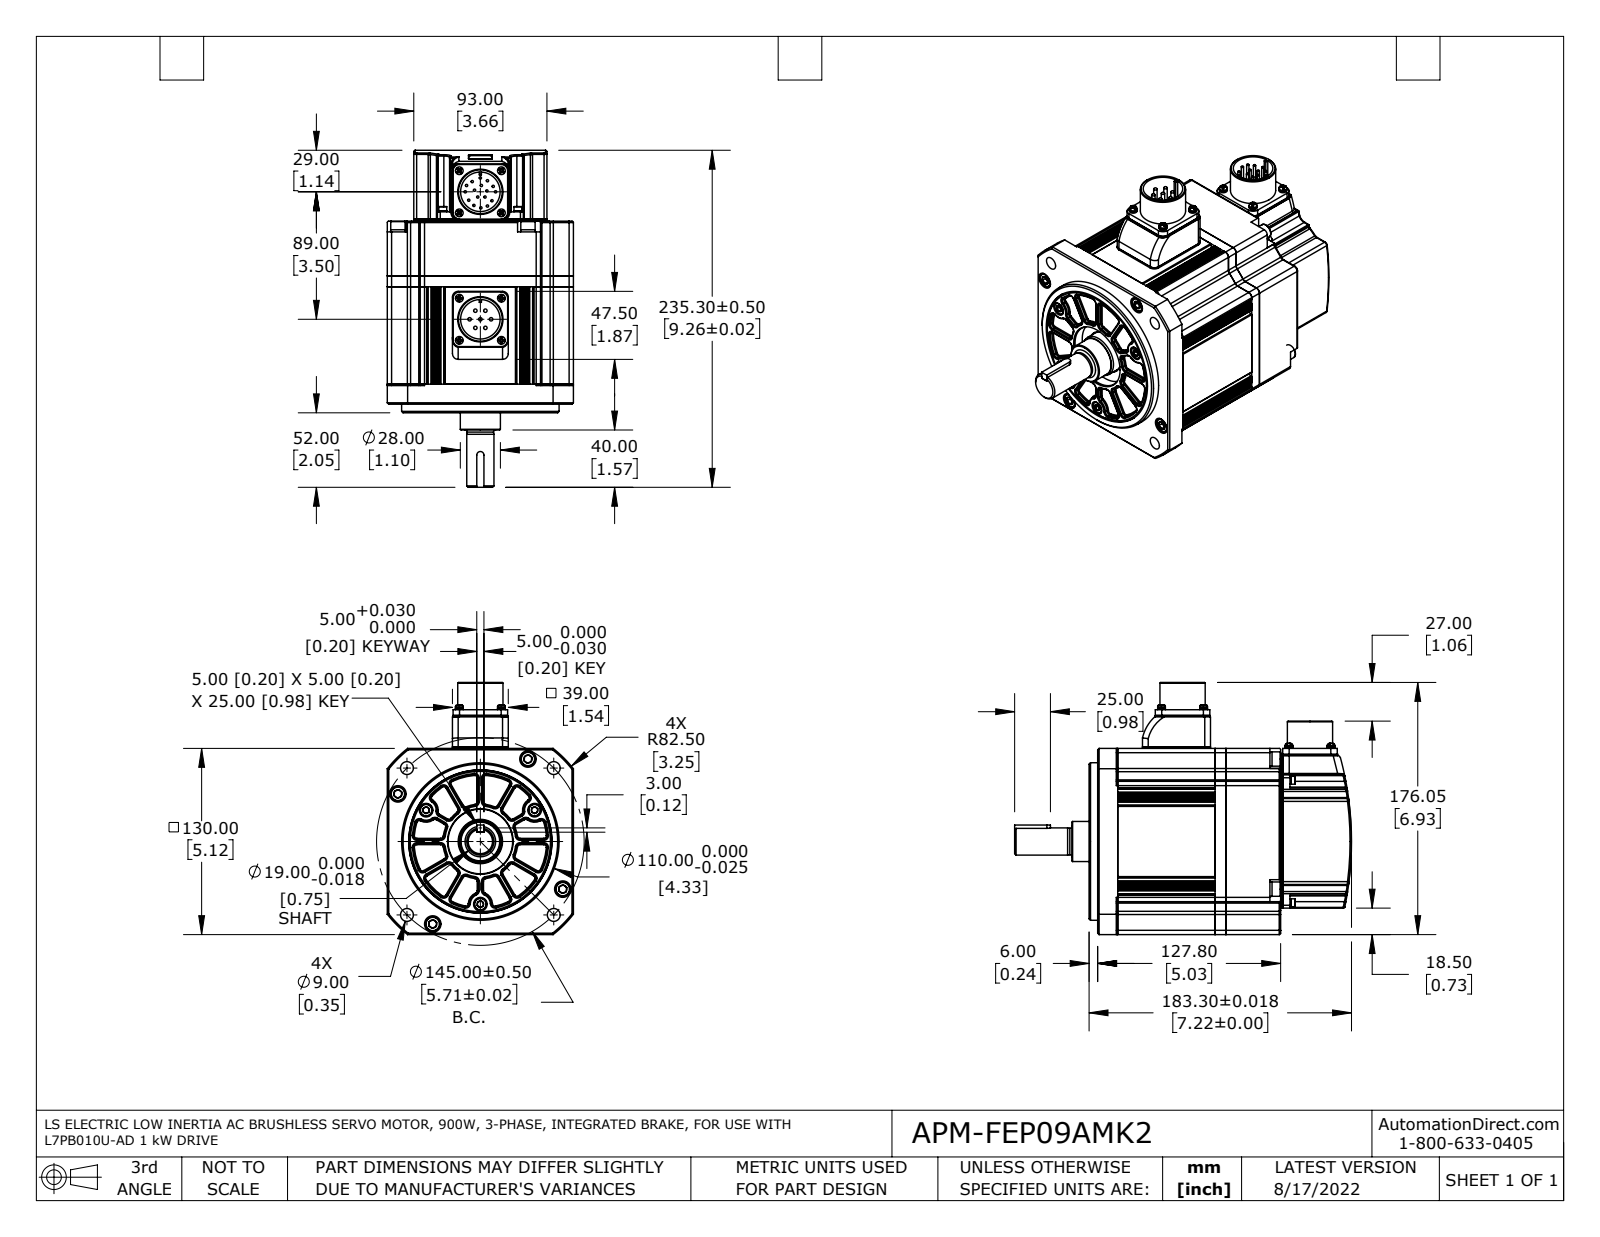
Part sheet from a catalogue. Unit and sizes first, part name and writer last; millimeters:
Units: millimetres
Overall size (bounding box): 235.3 × 176 × 130
Round holes (diameter × count): ⌀2.5 ×12, ⌀3 ×8, ⌀3 ×8, ⌀3.5 ×8, ⌀5 ×7, ⌀3.6 ×4, ⌀3.7 ×4, ⌀6.8 ×4, ⌀7 ×4, ⌀9 ×4, ⌀11.5 ×4, ⌀5.6 ×3
Round bosses / shafts (diameter × count): ⌀1.6 ×17, ⌀5.4 ×8, ⌀2.4 ×7, ⌀10.2 ×4, ⌀10 ×4, ⌀6 ×4, ⌀5.5 ×4, ⌀3 ×4
Partial cylindrical surfaces — rounded edges, fillets, slot ends (radius × count): R0.5 ×72, R2.5 ×55, R0.7 ×24, R1 ×22, R2 ×17, R3 ×16, R4.5 ×12, R4 ×8
Main face-to-face distances: 68, 7.6, 75.6, 1, 130, 115.3, 38.7, 46.3, 114.3, 39.7
Hole centre spacings: 20.8, 29.4, 89, 19.1, 26.4, 41.6, 50.2, 66.5
Volume: 2 397 000 mm³ · Surface area: 330 500 mm²
Bodies: 57 solids, 2211 faces (729 planar, 841 cylindrical, 641 other)
Part name (STEP PRODUCT): FMP13GA003G01_Out Line(APM-FEP09A_K2) r1 nc fxt
STEP written by: SolidWorks 2017 (AUTOMOTIVE_DESIGN)
